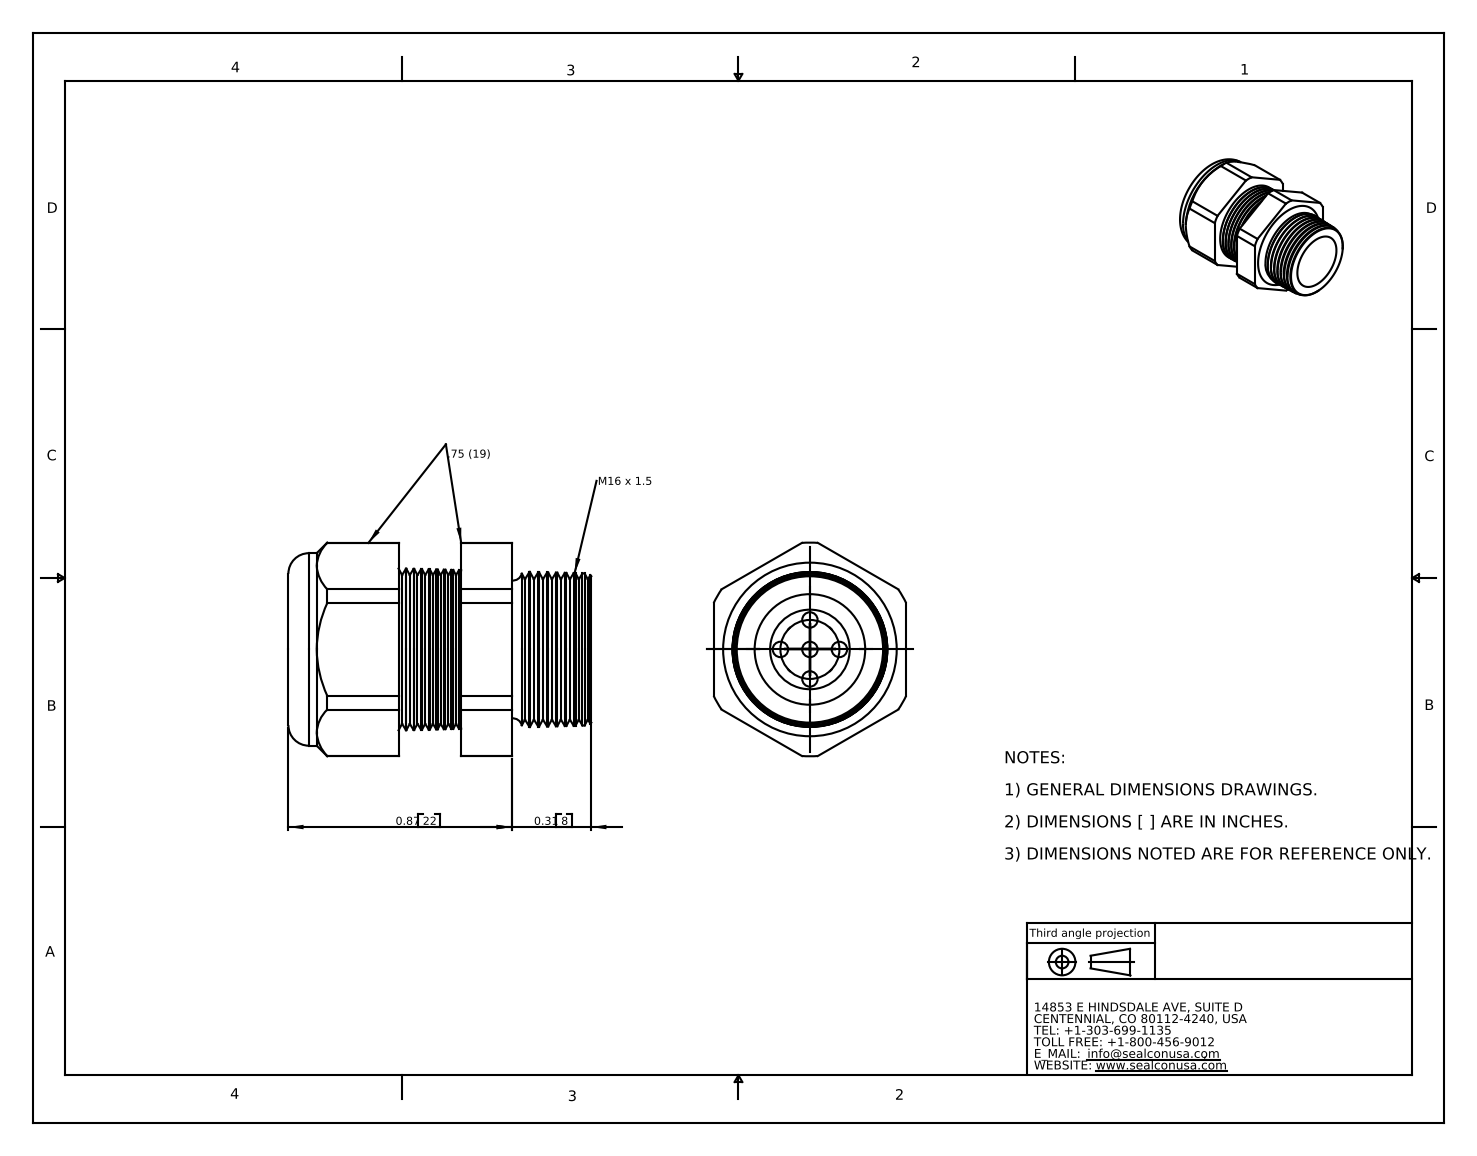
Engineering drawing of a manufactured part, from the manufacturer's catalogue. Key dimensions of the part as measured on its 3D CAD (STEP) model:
Part name (STEP PRODUCT): CD16M3-BK
STEP written by: SolidWorks 2007 (CONFIG_CONTROL_DESIGN)
Units: inches
Bodies: 2 solids, 160 faces (20 planar, 30 cylindrical, 110 other)
Overall size (bounding box): 1.18 × 0.833 × 0.75
Volume: 0.336 in³ · Surface area: 6.204 in²
Round holes (diameter × count): ⌀0.06 ×5, ⌀0.29 ×1, ⌀0.31 ×1
Round bosses / shafts (diameter × count): ⌀0.75 ×1
Partial cylindrical surfaces — rounded edges, fillets, slot ends (radius × count): R0.416 ×1
Main face-to-face distances: 0.75, 0.673, 0.75, 0.429, 0.244, 0.87, 0.441, 0.197, 1.18, 0.751
Hole centre spacings: 0.115, 0.163, 0.23
